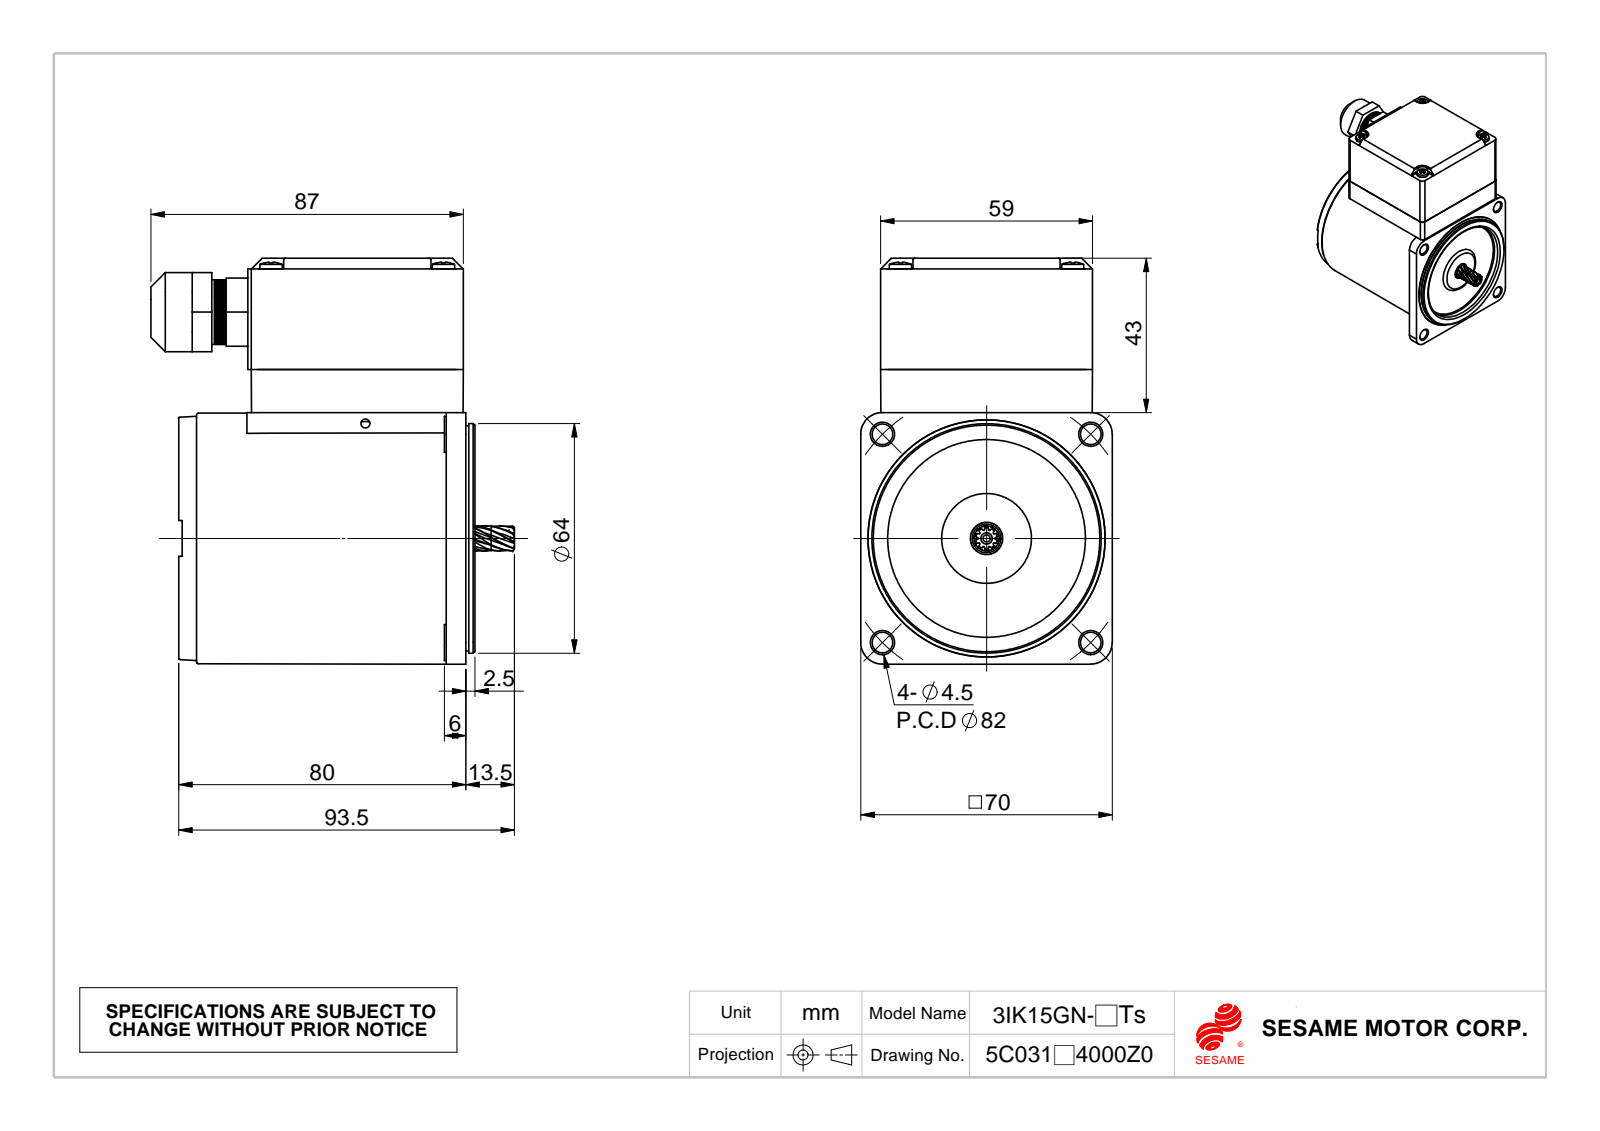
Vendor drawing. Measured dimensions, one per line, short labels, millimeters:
name: Ts下墊片; M315Ts_2車工; C364_車工(成品); 15GN_0.成品 (+1 more)
written by: SolidWorks 2010 (CONFIG_CONTROL_DESIGN)
unit: mm
bodies: 11 solids, 2439 faces (199 planar, 806 cylindrical, 1434 other)
size: 113 × 101.25 × 70
volume: 468 442 mm³; area: 72 673 mm²
holes: 4× ⌀3.3, 4× ⌀3.5, 4× ⌀3.9, 4× ⌀4.3, 4× ⌀5.75, 1× ⌀2, 1× ⌀2.5, 1× ⌀9, 1× ⌀11, 1× ⌀12, 1× ⌀14.5, 1× ⌀18
bosses: 4× ⌀10, 4× ⌀6.3, 4× ⌀3, 1× ⌀63.93, 1× ⌀62.73, 1× ⌀57.42, 1× ⌀57.2, 1× ⌀22
rounds: 12× R2, 8× R0.5, 6× R4, 4× R1.5, 4× R3, 4× R3.5, 4× R6, 1× R34.25
face distances: 12, 0.75, 77.4, 1.5, 77.5, 31, 43, 59, 75.89, 1.51
hole spacings: 41.01, 48, 58, 11.67, 12.35, 12.7, 24.93, 25
